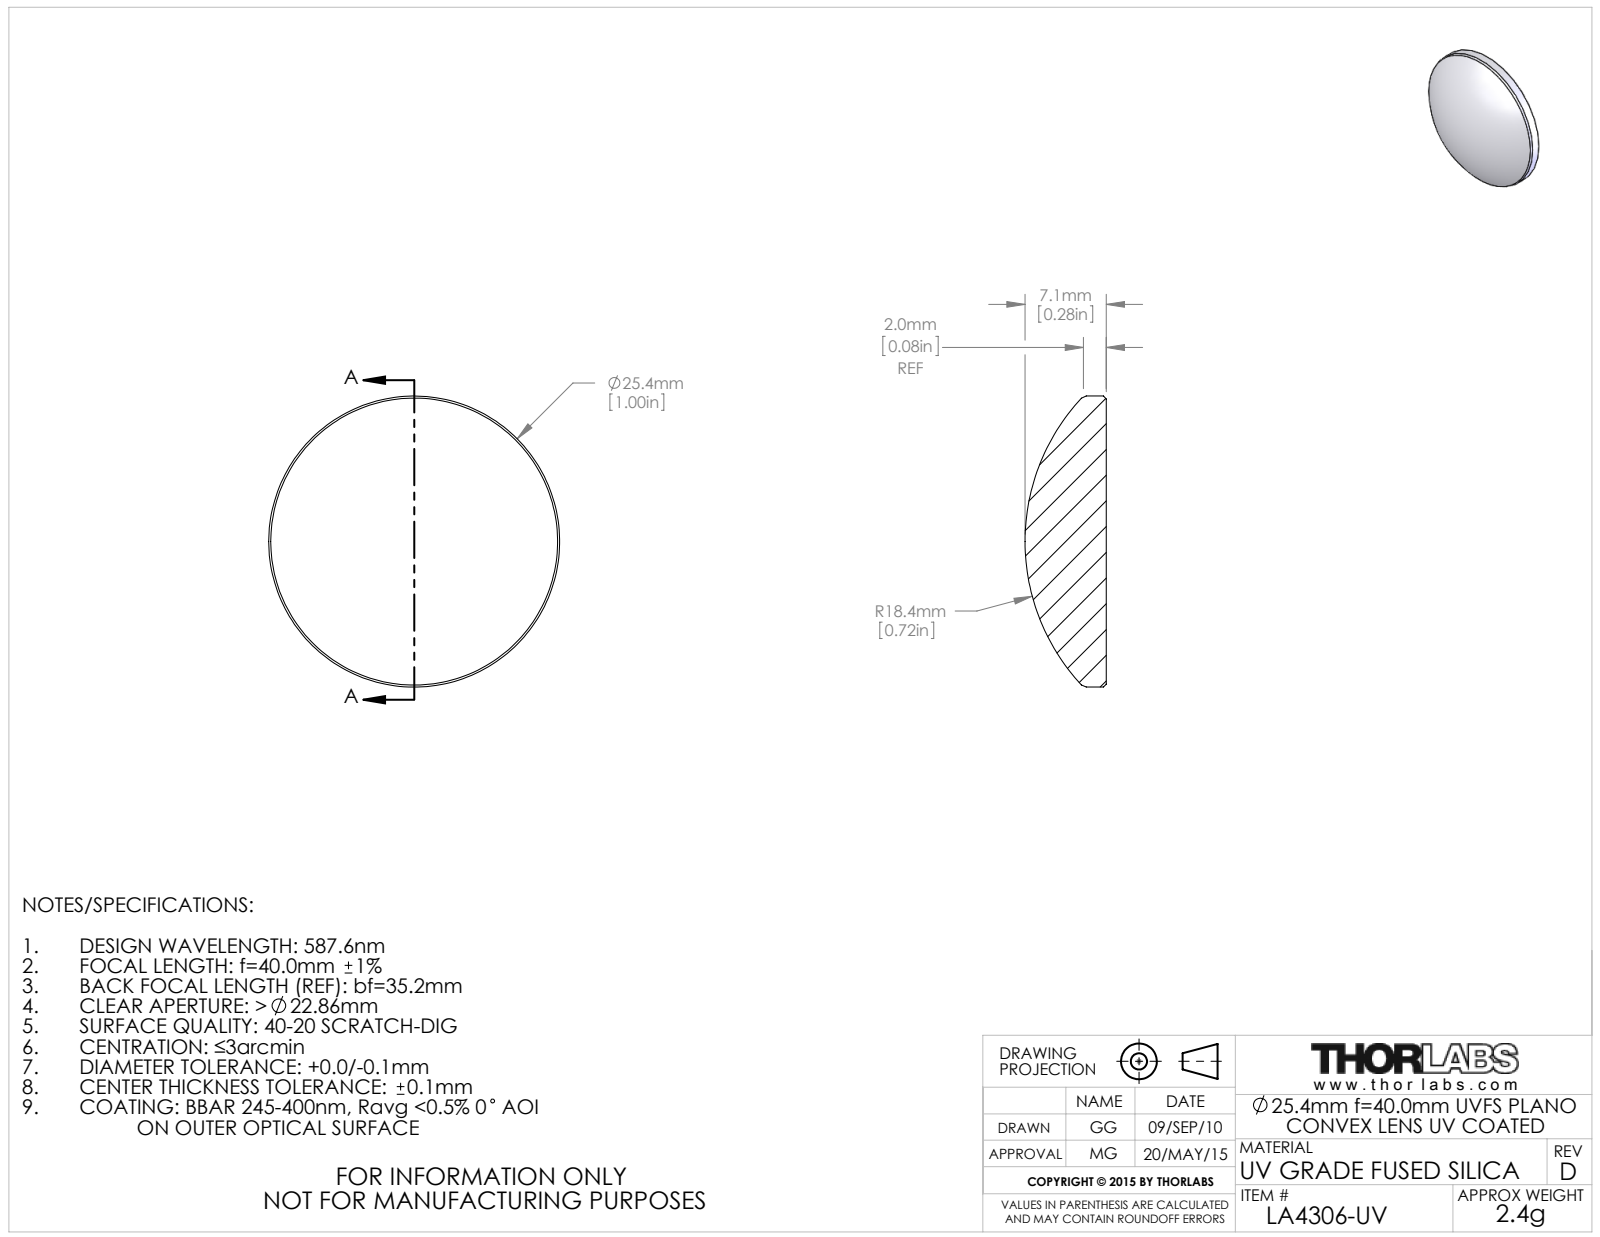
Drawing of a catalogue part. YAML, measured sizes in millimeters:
part_name: "4279-E0W"
step_written_by: "SolidWorks 2014 (CONFIG_CONTROL_DESIGN)"
units: millimeters
bodies: {solids: 1, faces: 9, planar: 1, cylindrical: 2, other: 6}
overall_size: [25.4, 25.4, 7.1]
volume: 2370
surface_area: 1239
round_bosses_or_shafts:
  - {diameter: 25.4, count: 1}
